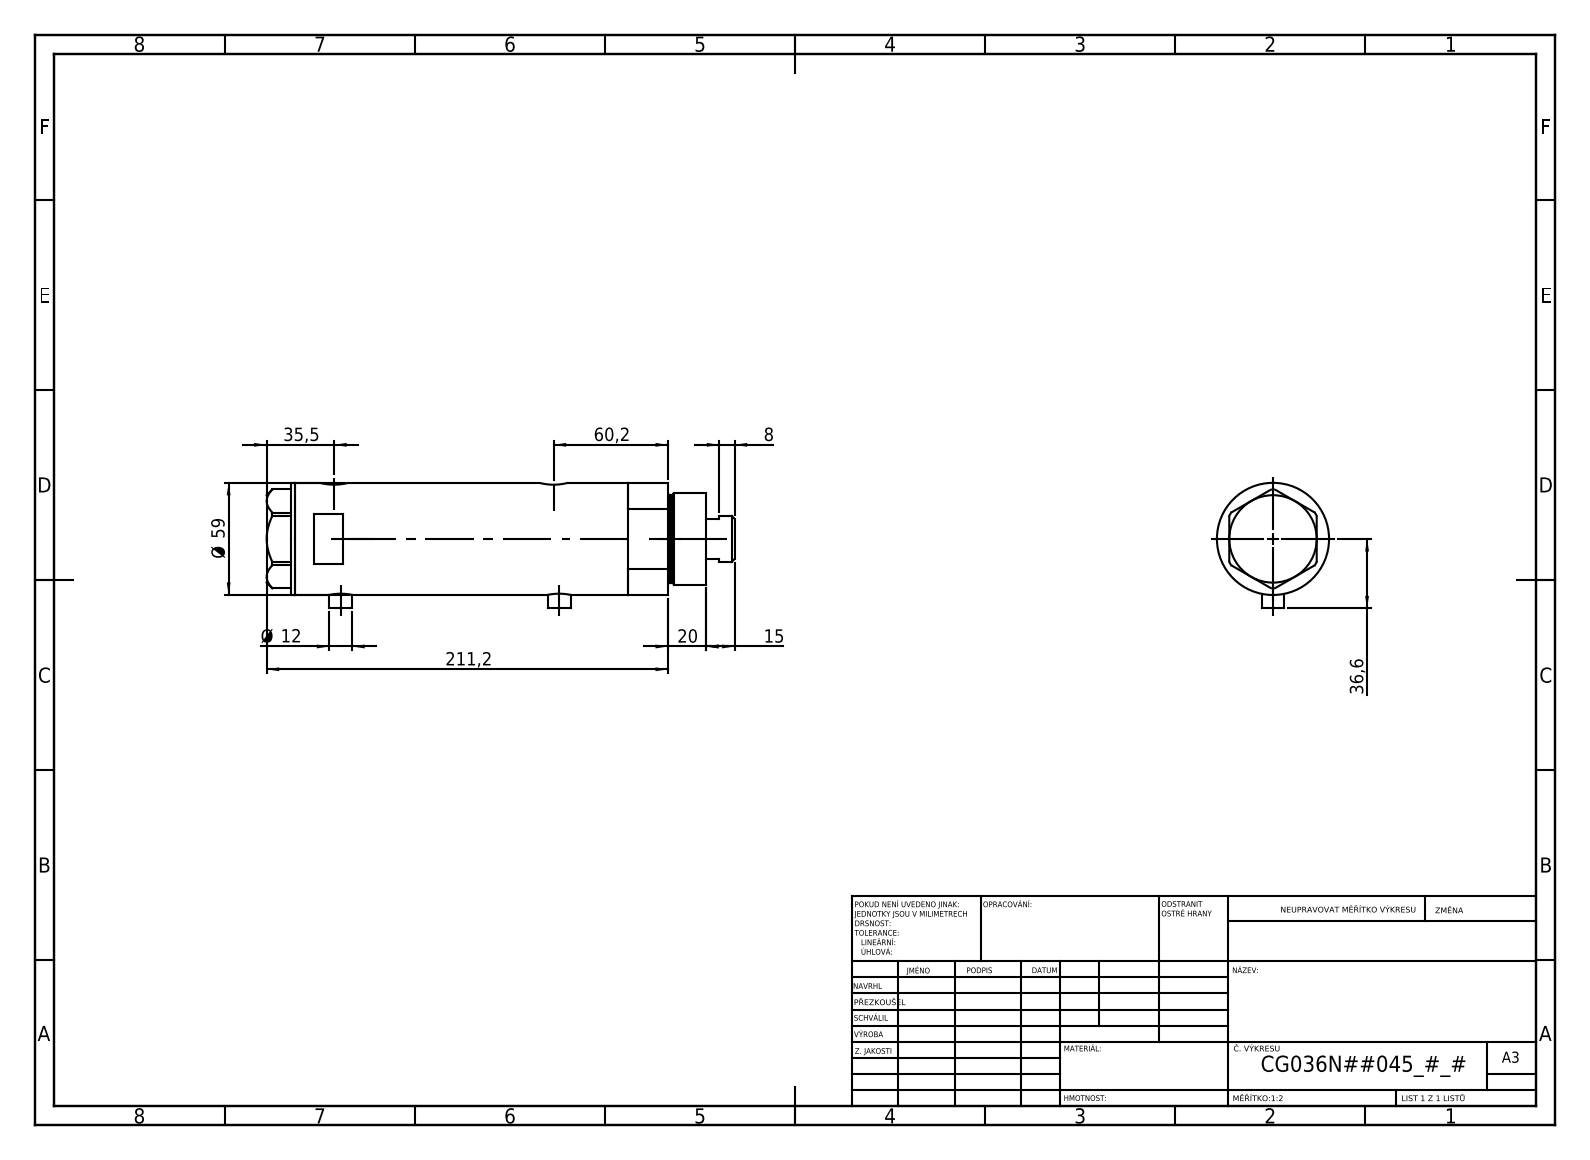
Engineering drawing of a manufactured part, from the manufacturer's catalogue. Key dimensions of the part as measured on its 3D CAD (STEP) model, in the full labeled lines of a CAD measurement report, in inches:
Part name (STEP PRODUCT): V270CG_FRONT; V270CG_BACK; V270CG_VC; V270CG_MIDDLE
STEP written by: SolidWorks 2019 (CONFIG_CONTROL_DESIGN)
Units: inches
Bodies: 4 solids, 120 faces (51 planar, 49 cylindrical, 20 other)
Overall size (bounding box): 9.693 × 2.602 × 2.323
Volume: 35.2 in³ · Surface area: 177.6 in²
Round holes (diameter × count): ⌀0.383 ×2, ⌀0.492 ×2, ⌀0.591 ×2, ⌀0.335 ×1, ⌀0.984 ×1, ⌀1.043 ×1, ⌀1.417 ×1, ⌀1.575 ×1, ⌀2.047 ×1
Round bosses / shafts (diameter × count): ⌀0.472 ×2, ⌀2.323 ×1, ⌀1.89 ×1, ⌀1.811 ×1, ⌀0.945 ×1
Main face-to-face distances: 5.402, 0.925, 4.476, 0.591, 1.516, 5.992, 0.079, 9.102, 8.512, 7.587
Hole centre spacings: 0.114, 0.138, 4.409, 4.524, 4.547, 4.661
